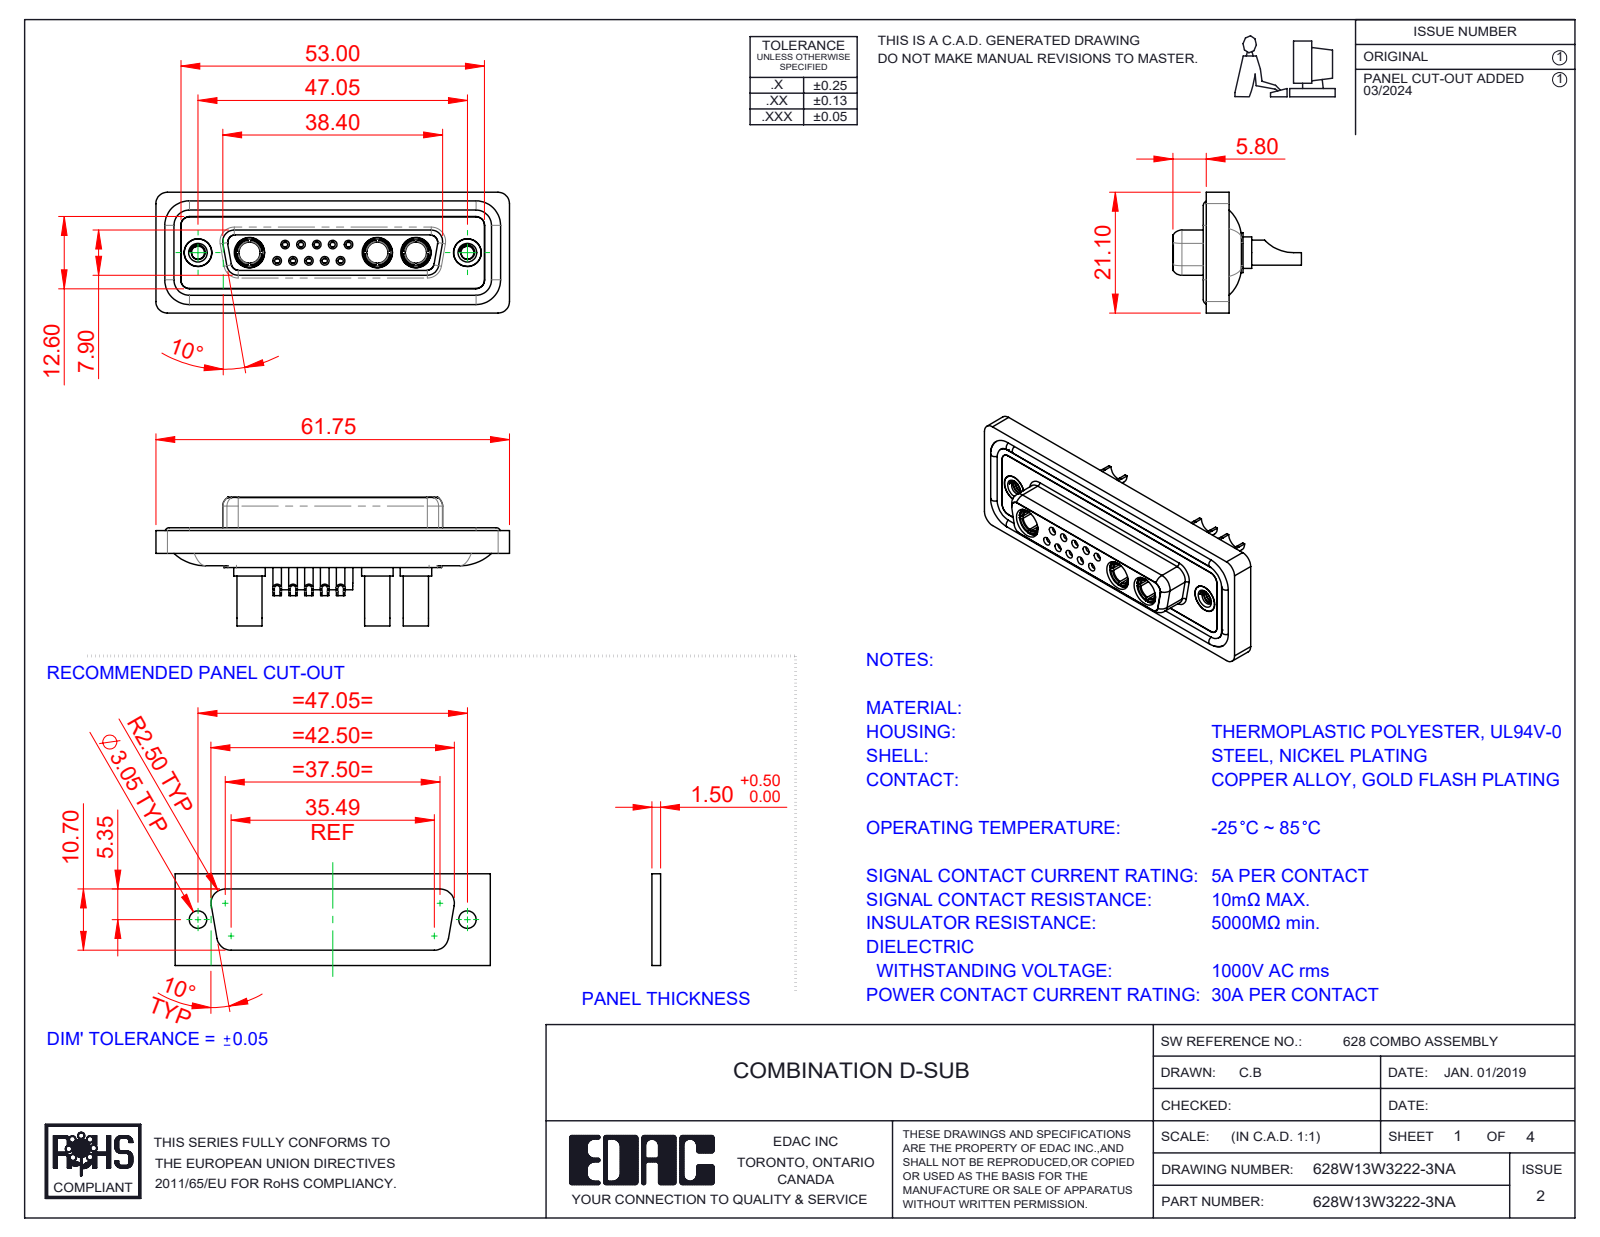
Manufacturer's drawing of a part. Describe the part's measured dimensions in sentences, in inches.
The part is named "628Combo Housing_13W3; Power Socket_30A SC; 628Combo Shell Front_25 Contacts; 628Combo Shell Rear_25 Contacts (+5 more)". Its 3-D file was written by "SolidWorks 2023 (CONFIG_CONTROL_DESIGN)". It is 23 solids with 1174 faces: 371 planar, 478 cylindrical and 325 other. Overall it measures 2.431 by 0.884 by 0.831 inches. Its volume is 0.511 cubic inches and its surface area 21.91 square inches. Round holes: 10 of diameter 0.035, 10 of diameter 0.039, 10 of diameter 0.043, 10 of diameter 0.059, 10 of diameter 0.079, 5 of diameter 0.063, 5 of diameter 0.067, 5 of diameter 0.191, 3 of diameter 0.138, 3 of diameter 0.146, 3 of diameter 0.209, 2 of diameter 0.089. Round bosses or shafts: 10 of diameter 0.087, 9 of diameter 0.063, 3 of diameter 0.217, 3 of diameter 0.205, 3 of diameter 0.195, 3 of diameter 0.187, 3 of diameter 0.173, 3 of diameter 0.148. Partial cylindrical surfaces (rounded edges, fillets, slot ends): 22 of radius 0.059, 18 of radius 0.079, 8 of radius 0.053, 8 of radius 0.063, 6 of radius 0.039, 4 of radius 0.01, 4 of radius 0.02, 4 of radius 0.024. The main face-to-face distances are 0.016, 0.071, 0.293, 0.222, 0.02, 0.26, 0.278, 0.063, 0.114, 0.043. The hole center spacings are 0.124, 0.109, 0.198, 0.198, 0.218, 0.327, 0.295, 0.109.
